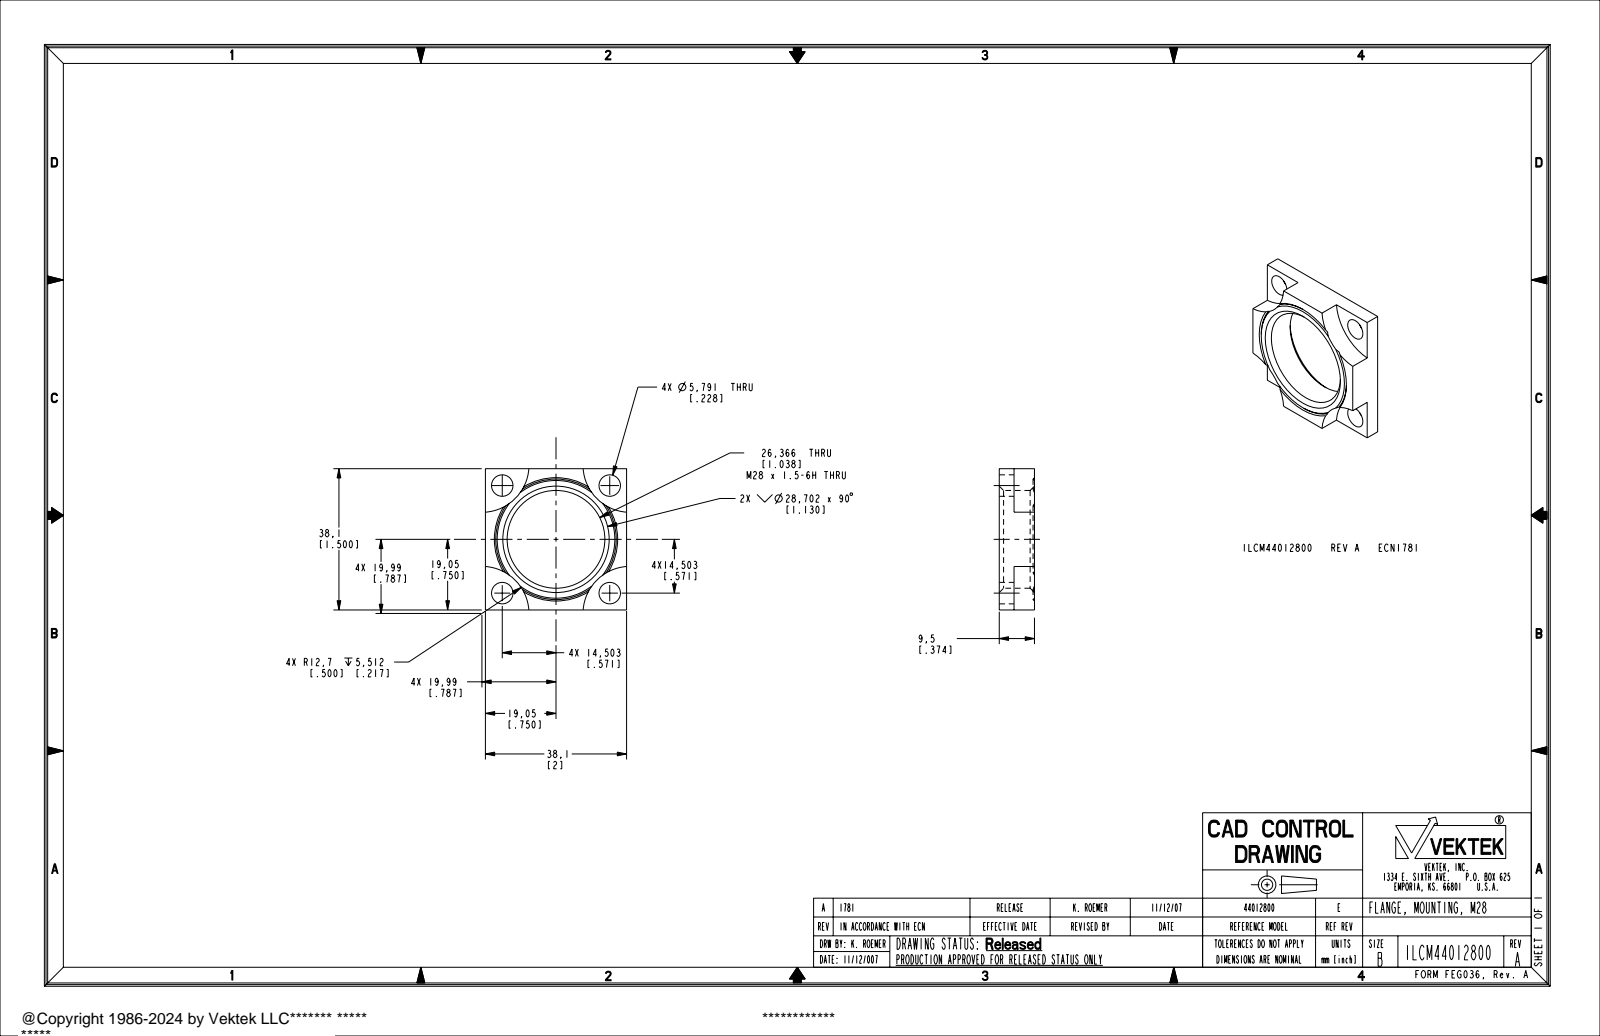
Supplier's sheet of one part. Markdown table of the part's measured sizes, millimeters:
| quantity | value |
| --- | --- |
| part name | ILCM44012800 |
| STEP written by | PRO/ENGINEER BY PARAMETRIC TECHNOLOGY CORPORATION, 2005180 (AUTOMOTIVE_DESIGN_CC2) |
| units | millimeters |
| bodies | 1 solid, 40 faces (14 planar, 14 cylindrical, 12 other) |
| overall size | 38.1 × 38.1 × 9.5 |
| volume | 5 769 mm³ |
| surface area | 3 919 mm² |
| round holes (diameter × count) | 5.79 × 4, 26.37 × 1 |
| partial cylindrical surfaces (radius × count) | 12.7 × 4 |
| main face-to-face distances | 38.1, 9.5, 5.51, 3.99 |
| hole center spacings | 20.51, 29, 41.01 |
